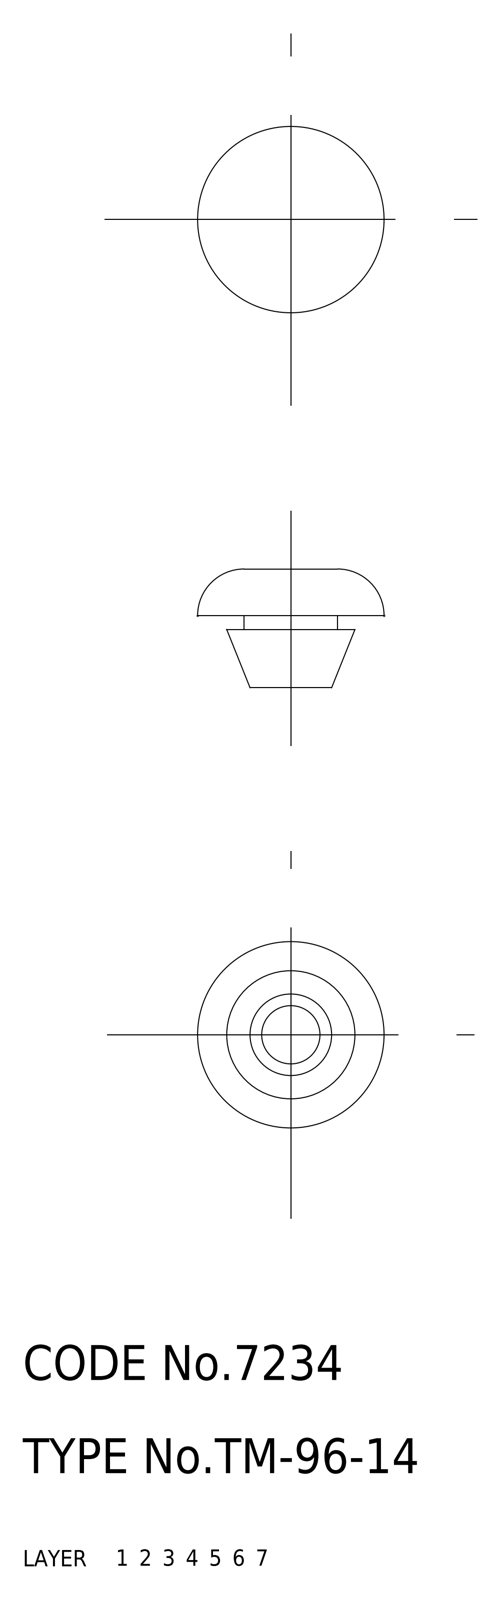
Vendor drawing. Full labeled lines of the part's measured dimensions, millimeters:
Part name (STEP PRODUCT): cushion
STEP written by: CADfix (AUTOMOTIVE_DESIGN)
Units: millimetres
Bodies: 1 solid, 13 faces (0 planar, 0 cylindrical, 13 other)
Overall size (bounding box): 16 × 16 × 10.2
Volume: 914 mm³ · Surface area: 823 mm²
